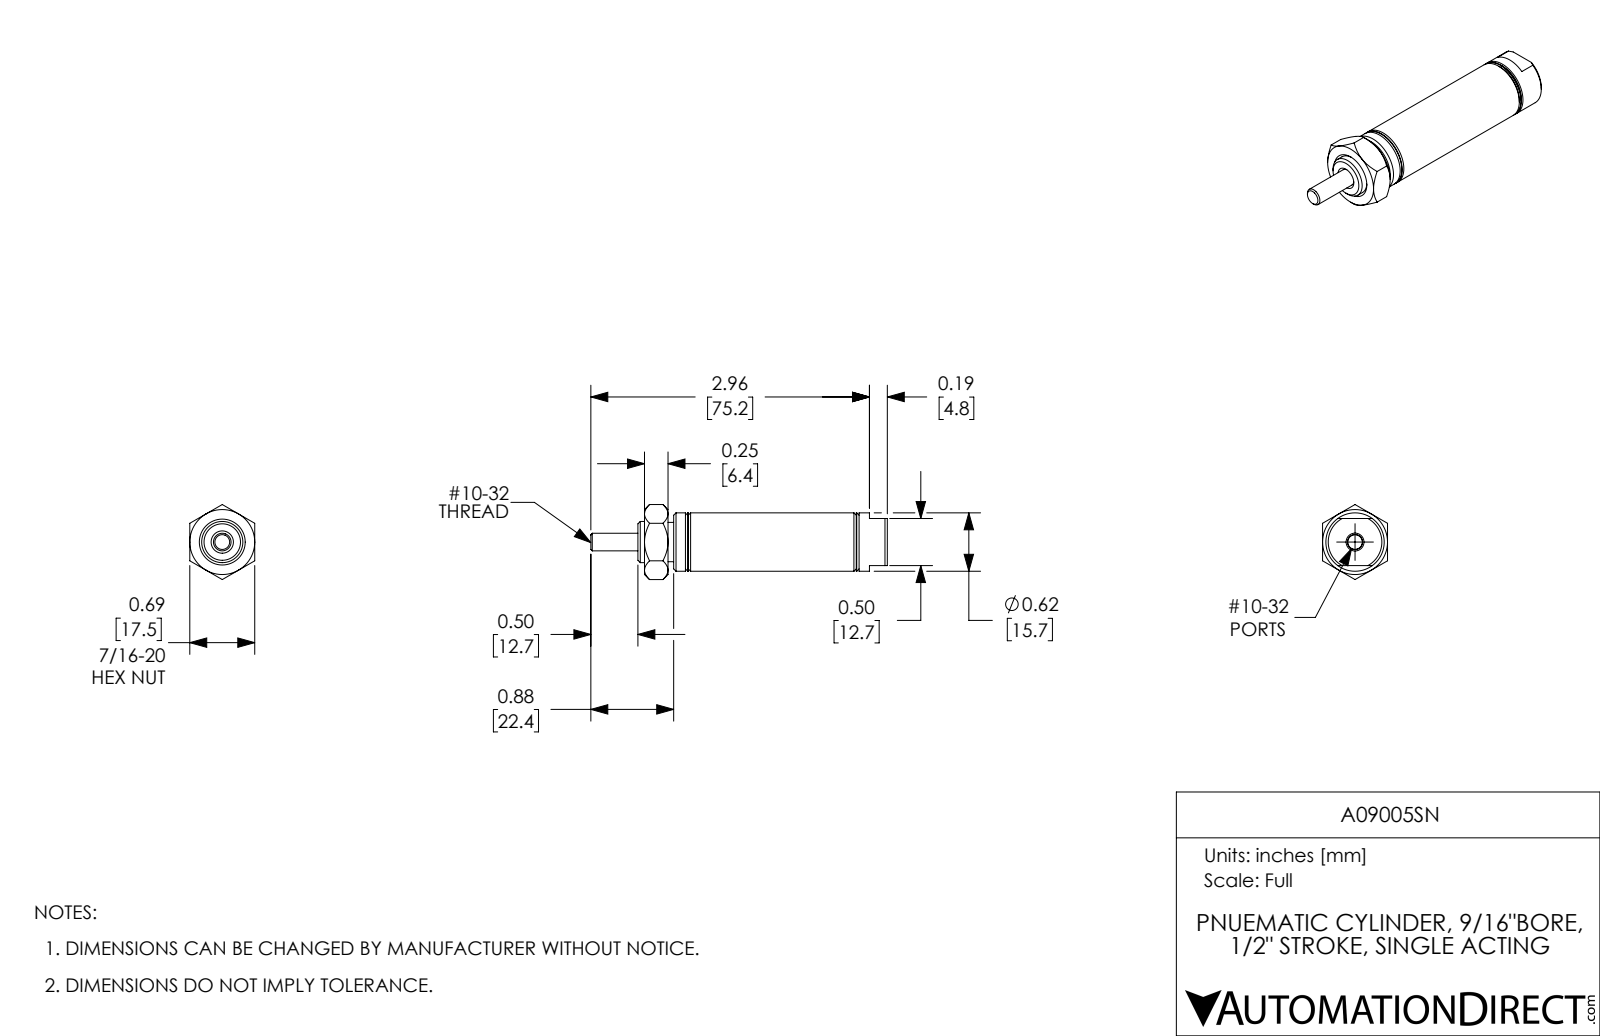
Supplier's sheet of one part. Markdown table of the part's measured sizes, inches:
| quantity | value |
| --- | --- |
| part name | A09005SN-MainBody; A09005SN_Mounting Nut_D-154; A09005SN-Rod; A09005SN |
| STEP written by | SolidWorks 2017 (AUTOMOTIVE_DESIGN) |
| units | inches |
| bodies | 3 solids, 95 faces (27 planar, 30 cylindrical, 38 other) |
| overall size | 3.15 × 0.797 × 0.69 |
| volume | 0.684 in³ |
| surface area | 12.74 in² |
| round holes (diameter × count) | 0.156 × 1, 0.159 × 1, 0.187 × 1, 0.19 × 1, 0.437 × 1, 0.563 × 1 |
| round bosses / shafts (diameter × count) | 0.62 × 1, 0.417 × 1 |
| main face-to-face distances | 0.5, 0.635, 1.635, 1.135, 0.69, 0.945, 1.445, 1, 2.33, 1.695 |
